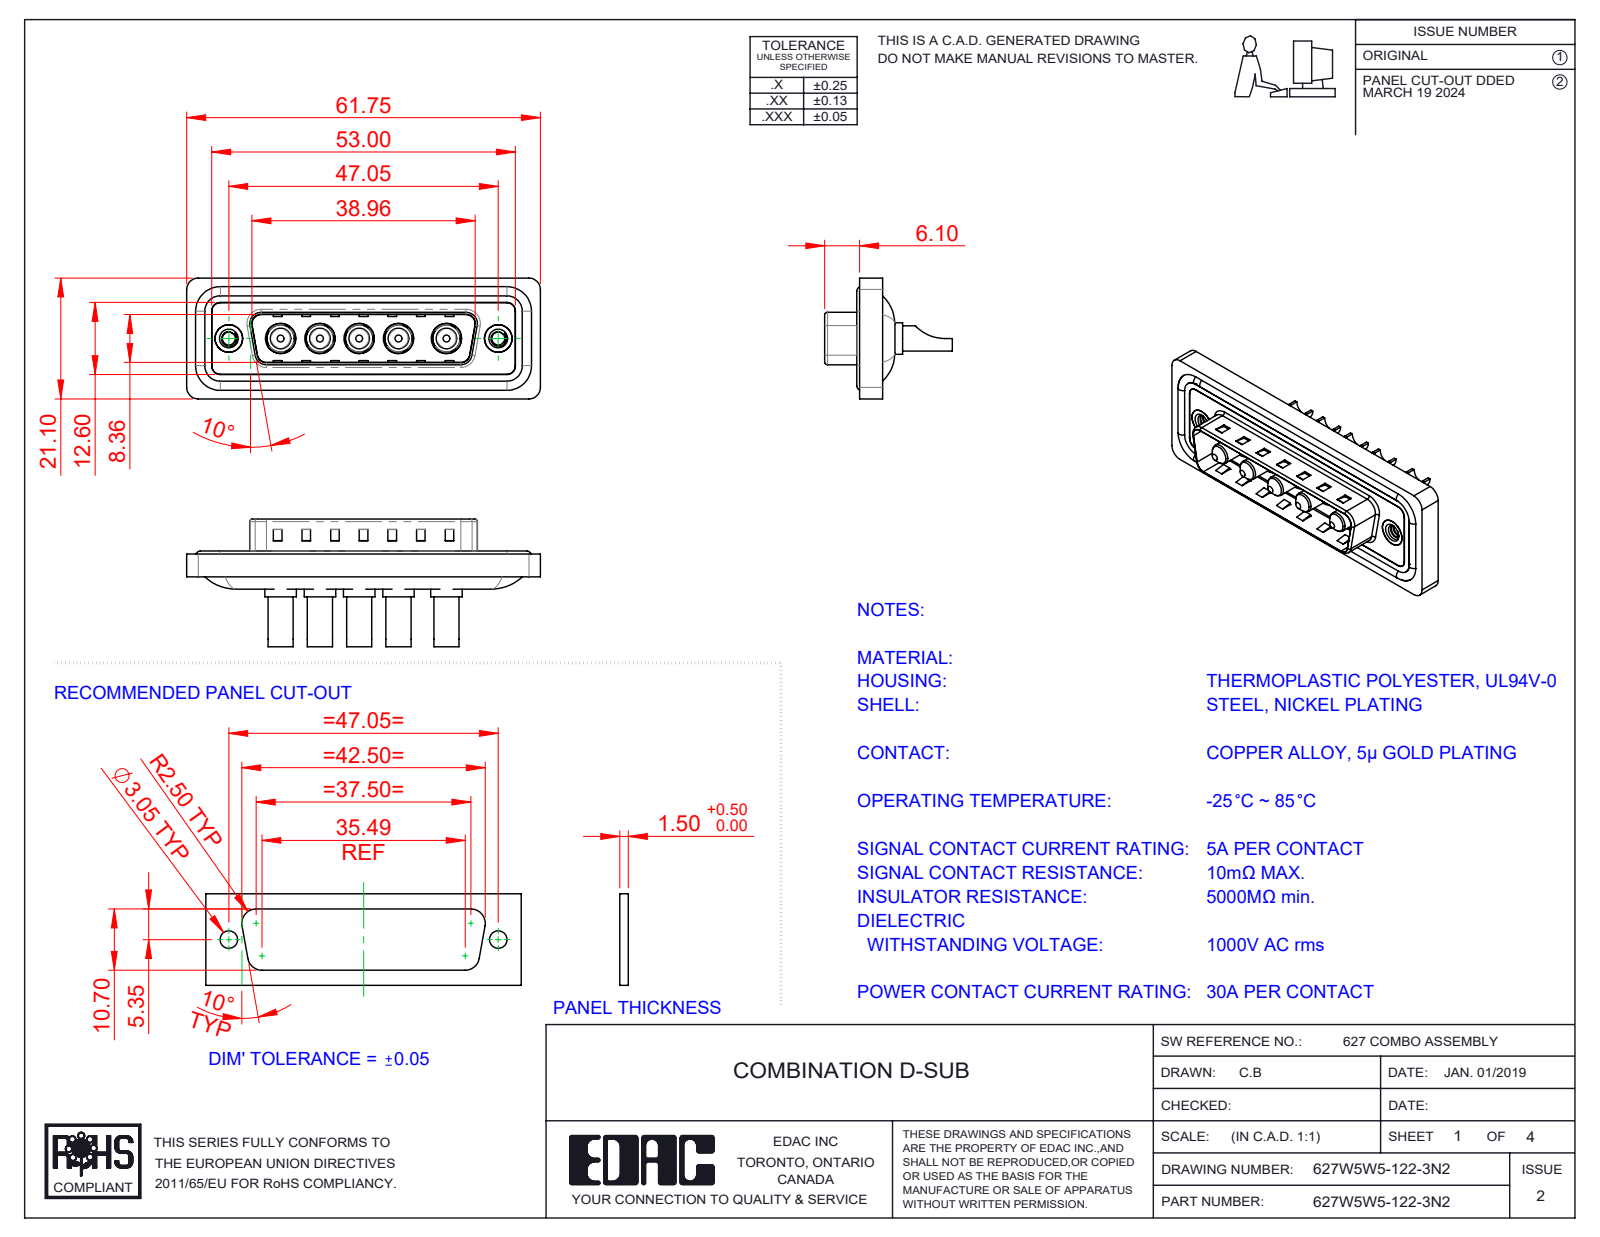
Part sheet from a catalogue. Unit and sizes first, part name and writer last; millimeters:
Units: millimetres
Overall size (bounding box): 61.75 × 22.3 × 21.1
Round holes (diameter × count): ⌀3.5 ×5, ⌀4.85 ×5, ⌀5.3 ×5, ⌀2.26 ×2, ⌀4 ×2, ⌀4.8 ×2, ⌀5 ×2
Round bosses / shafts (diameter × count): ⌀5.5 ×5, ⌀5.2 ×5, ⌀4.75 ×5, ⌀4.4 ×5, ⌀3.75 ×5, ⌀3.6 ×5, ⌀1.6 ×4, ⌀4.9 ×2
Partial cylindrical surfaces — rounded edges, fillets, slot ends (radius × count): R1.5 ×22, R2 ×18, R0.5 ×8, R1.6 ×8, R2.1 ×5, R0.25 ×4, R0.6 ×4, R0.65 ×4
Main face-to-face distances: 0.4, 1.5, 0.5, 1.1, 3.1, 1.6, 2.9, 0.82, 9.58, 5.65
Hole centre spacings: 6.86, 9.04, 13.73, 38.01, 6.87, 8.37, 8.38, 9.05
Volume: 7 593 mm³ · Surface area: 12 334 mm²
Bodies: 17 solids, 708 faces (274 planar, 298 cylindrical, 136 other)
Part name (STEP PRODUCT): Power Pin_30A SC; 627W5W5-122-3N2; 627Combo Waterproof Housing_25 Contacts; 627Combo Shell Front_25 Contacts (+3 more)
STEP written by: SolidWorks 2023 (CONFIG_CONTROL_DESIGN)
